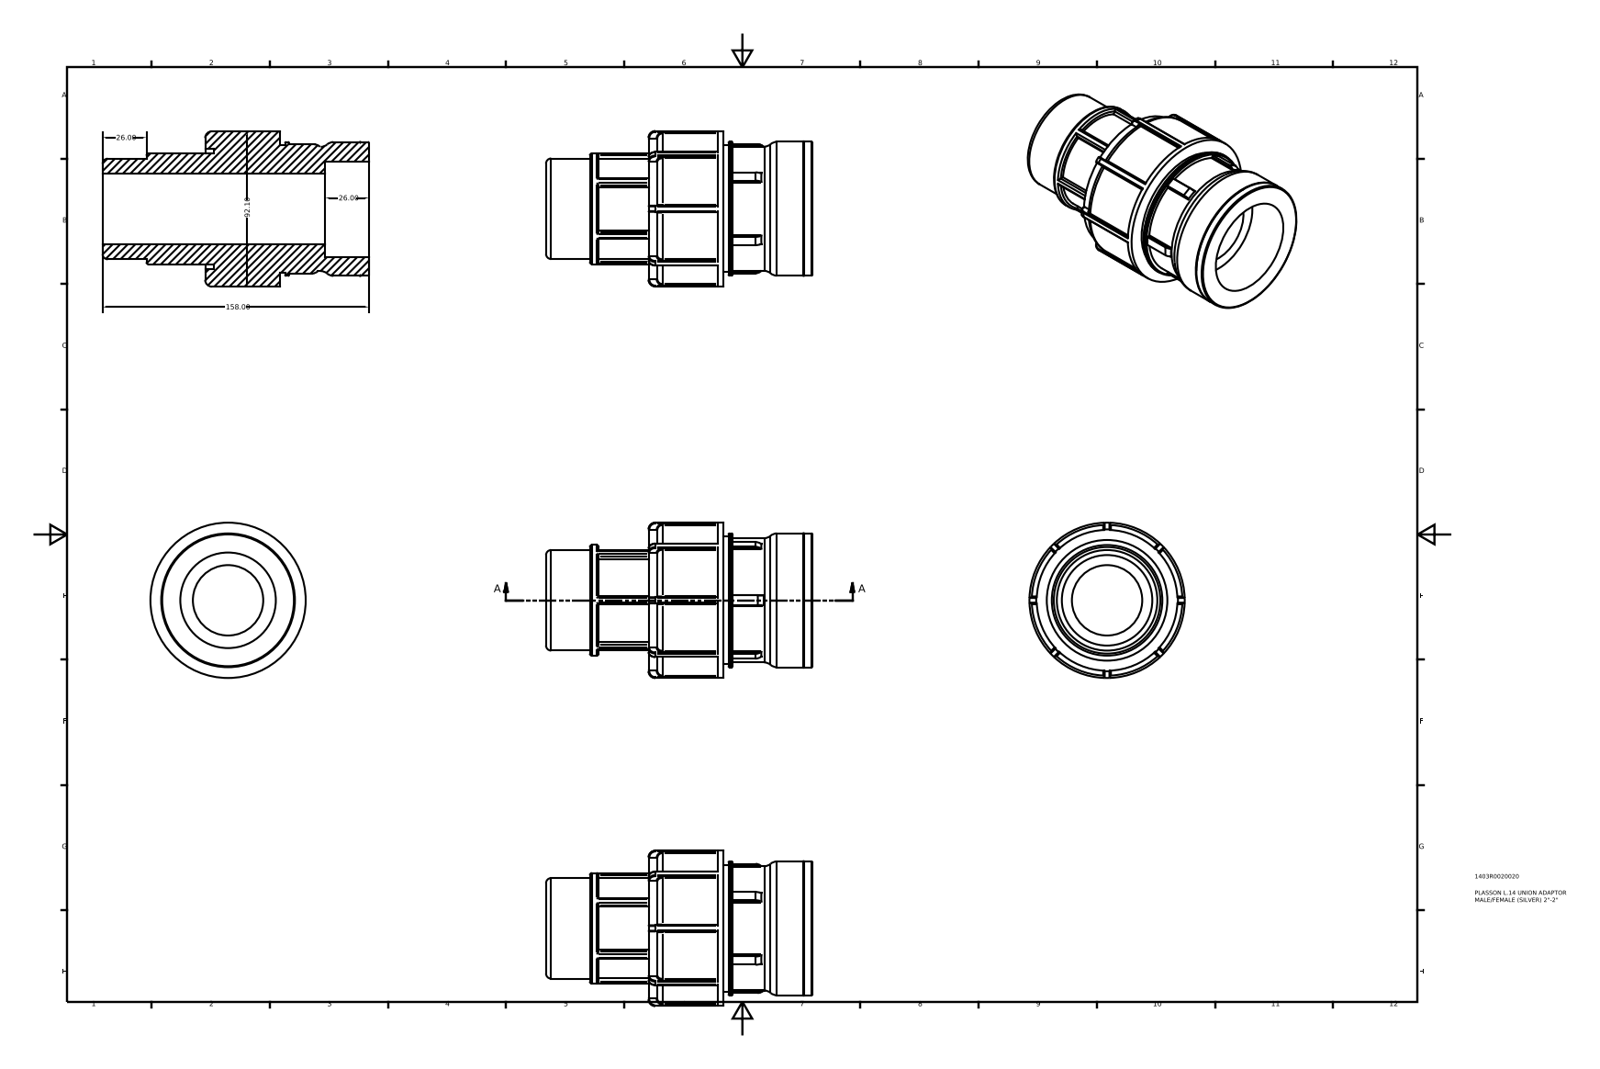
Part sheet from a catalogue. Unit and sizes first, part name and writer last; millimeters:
Units: millimetres
Overall size (bounding box): 158 × 92.1 × 92.1
Round holes (diameter × count): ⌀41.73 ×1, ⌀56.66 ×1, ⌀71.54 ×1
Round bosses / shafts (diameter × count): ⌀92.1 ×1, ⌀89.34 ×1, ⌀83.46 ×1, ⌀79.32 ×1, ⌀75.35 ×1, ⌀73.65 ×1, ⌀65.58 ×1, ⌀59.61 ×1
Partial cylindrical surfaces — rounded edges, fillets, slot ends (radius × count): R0.46 ×44, R0.57 ×12, R1.19 ×12, R4.61 ×5
Main face-to-face distances: 52.93, 26, 44.24, 97.17, 5.2, 132, 71.17, 26.93, 39.04, 65.97
Volume: 444 102 mm³ · Surface area: 75 288 mm²
Bodies: 1 solid, 243 faces (69 planar, 110 cylindrical, 64 other)
Part name (STEP PRODUCT): 1403R0020020
STEP written by: Autodesk Inventor 2015 (AUTOMOTIVE_DESIGN)
